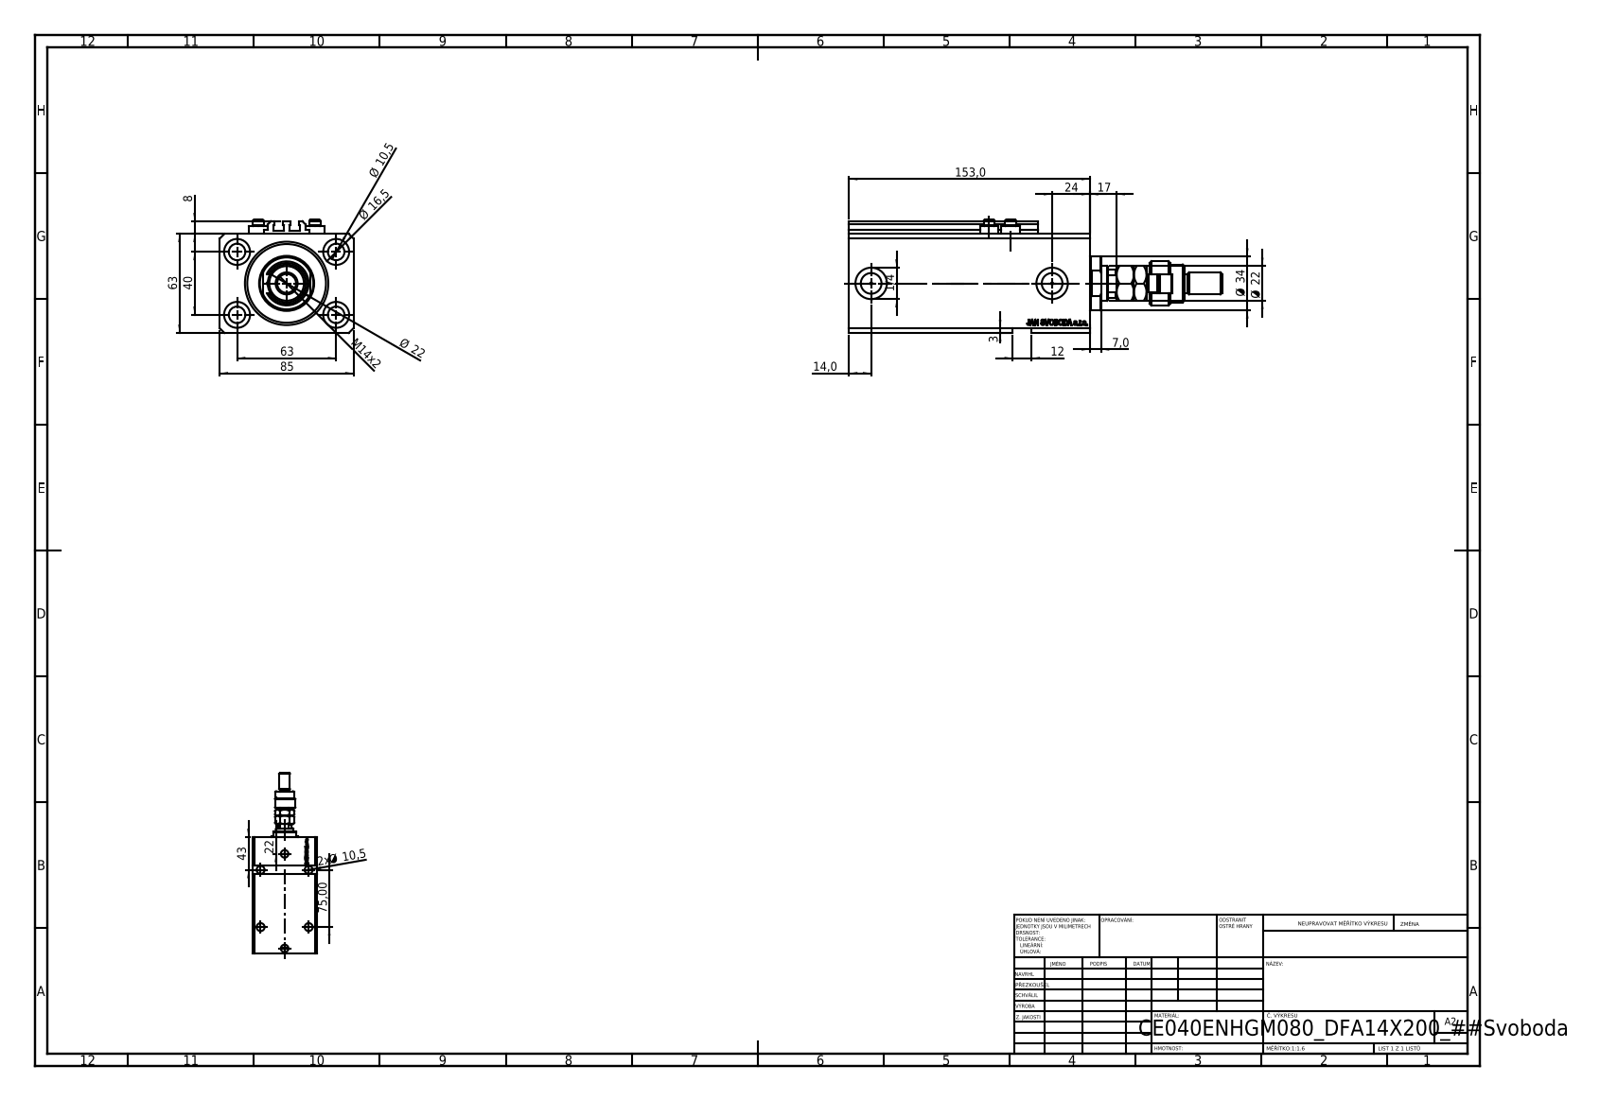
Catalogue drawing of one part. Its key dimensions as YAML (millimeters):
part_name: "FEMALE_PART_FOR_DFA; V250CE_C_VCP; V250CE_E_Body; MFA (+2 more)"
step_written_by: "SolidWorks 2019 (CONFIG_CONTROL_DESIGN)"
units: millimeters
bodies: {solids: 10, faces: 1192, planar: 563, cylindrical: 159, other: 470}
overall_size: [237, 85, 72]
volume: 705763
surface_area: 148784
round_holes:
  - {diameter: 10.5, count: 8}
  - {diameter: 1.25, count: 4}
  - {diameter: 4, count: 4}
  - {diameter: 16.5, count: 4}
  - {diameter: 10, count: 2}
  - {diameter: 13.16, count: 2}
  - {diameter: 20, count: 2}
  - {diameter: 12.5, count: 1}
  - {diameter: 22, count: 1}
  - {diameter: 40, count: 1}
  - {diameter: 53, count: 1}
round_bosses_or_shafts:
  - {diameter: 11.6, count: 4}
  - {diameter: 7, count: 4}
  - {diameter: 34, count: 1}
  - {diameter: 28, count: 1}
  - {diameter: 24, count: 1}
  - {diameter: 18, count: 1}
  - {diameter: 14, count: 1}
  - {diameter: 12, count: 1}
partial_cylinders:
  - {radius: 0.2, count: 10}
  - {radius: 9.75, count: 1}
  - {radius: 10.5, count: 1}
face_to_face_distances: [63, 85, 17, 153, 136, 11.4, 124.6, 141.6, 3, 65]
hole_center_spacings: [37.31, 63, 13.6, 15.4, 24.96, 33.62, 36, 37.86]
